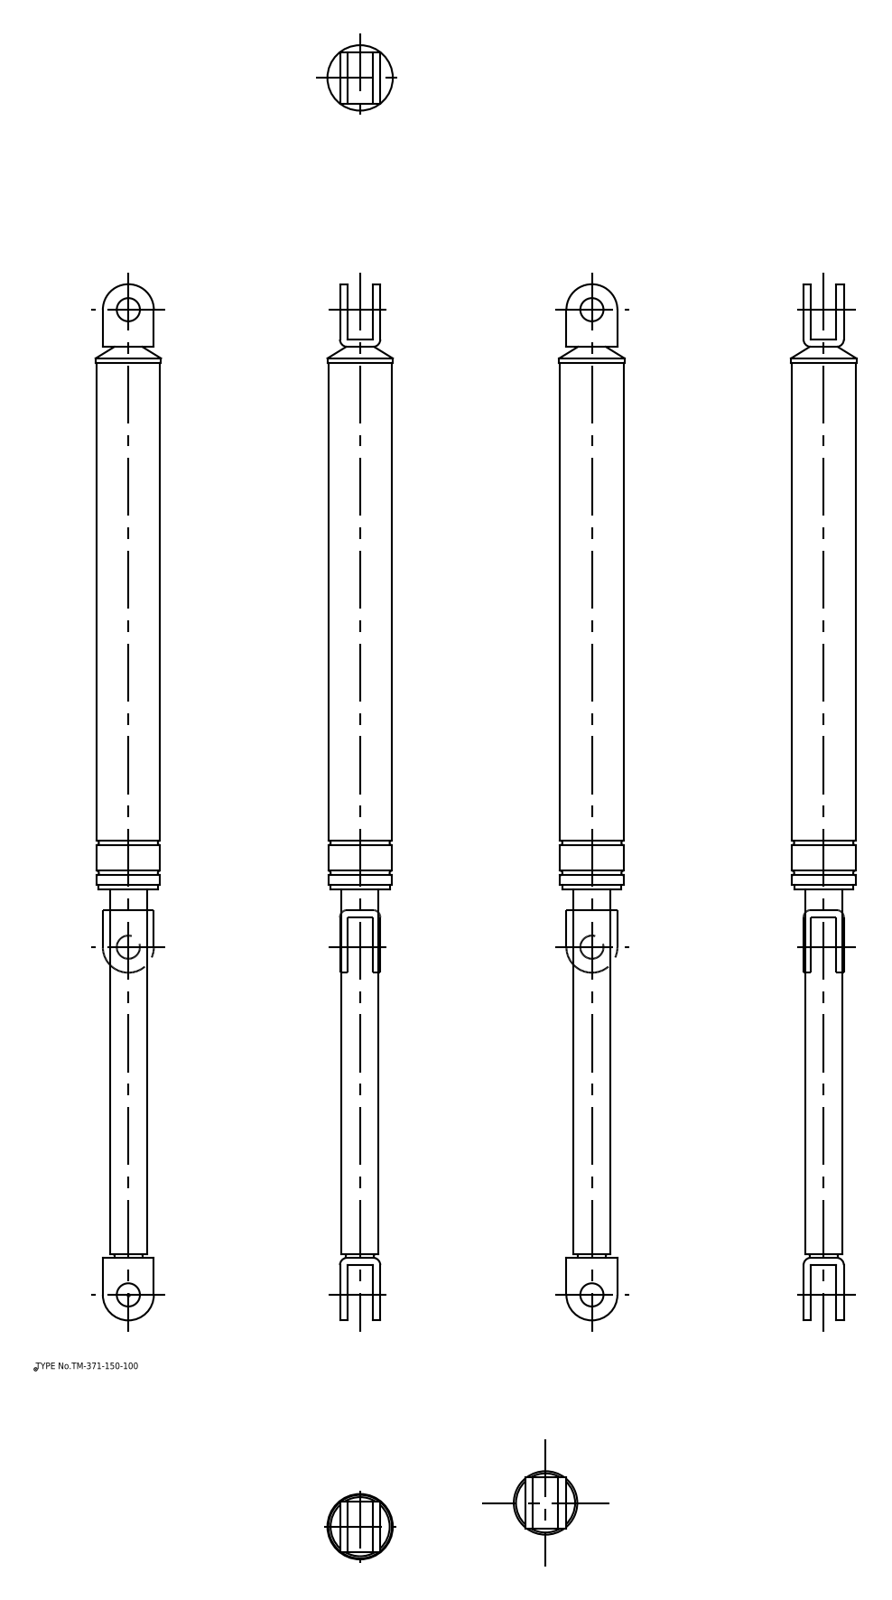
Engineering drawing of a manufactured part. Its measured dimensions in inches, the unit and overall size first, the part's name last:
Units: inches
Overall size (bounding box): 17.598 × 1.11 × 1.11
Round holes (diameter × count): ⌀0.394 ×2
Round bosses / shafts (diameter × count): ⌀1.11 ×1, ⌀1.079 ×1, ⌀1.004 ×1, ⌀0.63 ×1, ⌀0.472 ×1
Partial cylindrical surfaces — rounded edges, fillets, slot ends (radius × count): R0.126 ×4, R0.433 ×2
Main face-to-face distances: 0.126, 0.559, 0.685, 0.433, 0.866, 15.598, 6.386, 15.724, 9.339, 9.213
Hole centre spacings: 16.732
Volume: 10.71 in³ · Surface area: 54.35 in²
Bodies: 2 solids, 69 faces (23 planar, 34 cylindrical, 12 other)
Part name (STEP PRODUCT): TM_371_150_100; TM_371_150_100_div
STEP written by: spGate 16.7.1 (AUTOMOTIVE_DESIGN)
